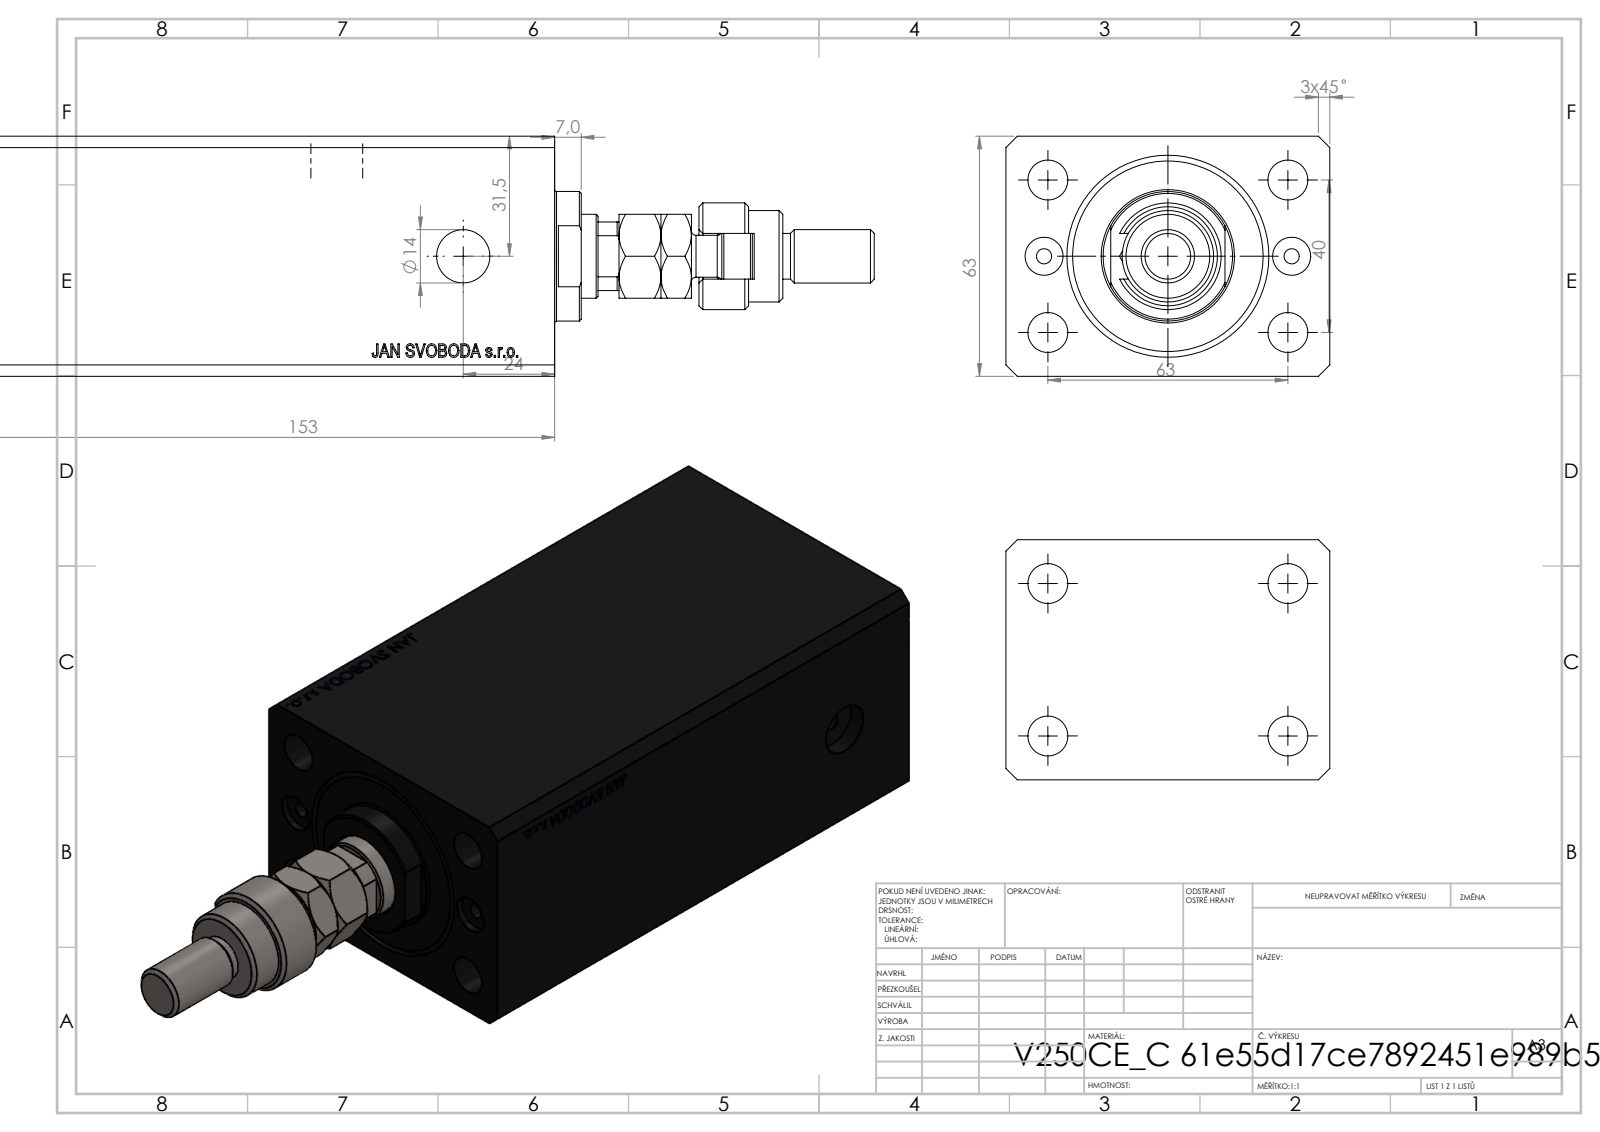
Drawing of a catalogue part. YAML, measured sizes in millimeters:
part_name: "FEMALE_PART_FOR_DFA; MFA; V250CE_C_Body; V250CE_VC_C (+1 more)"
step_written_by: "SolidWorks 2019 (CONFIG_CONTROL_DESIGN)"
units: millimeters
bodies: {solids: 5, faces: 949, planar: 456, cylindrical: 57, other: 436}
overall_size: [237, 85, 63]
volume: 718817
surface_area: 128557
round_holes:
  - {diameter: 4, count: 4}
  - {diameter: 10.5, count: 4}
  - {diameter: 10, count: 2}
  - {diameter: 14, count: 2}
  - {diameter: 12.5, count: 1}
  - {diameter: 22, count: 1}
  - {diameter: 40, count: 1}
  - {diameter: 53, count: 1}
round_bosses_or_shafts:
  - {diameter: 34, count: 1}
  - {diameter: 28, count: 1}
  - {diameter: 24, count: 1}
  - {diameter: 18, count: 1}
  - {diameter: 14, count: 1}
  - {diameter: 12, count: 1}
  - {diameter: 11, count: 1}
partial_cylinders:
  - {radius: 9.75, count: 1}
  - {radius: 10.5, count: 1}
face_to_face_distances: [63, 85, 153, 17, 136, 11.4, 124.6, 141.6, 100.4, 80]
hole_center_spacings: [20.02, 37.31, 67.05, 32.5, 40, 63, 74.63, 65]
